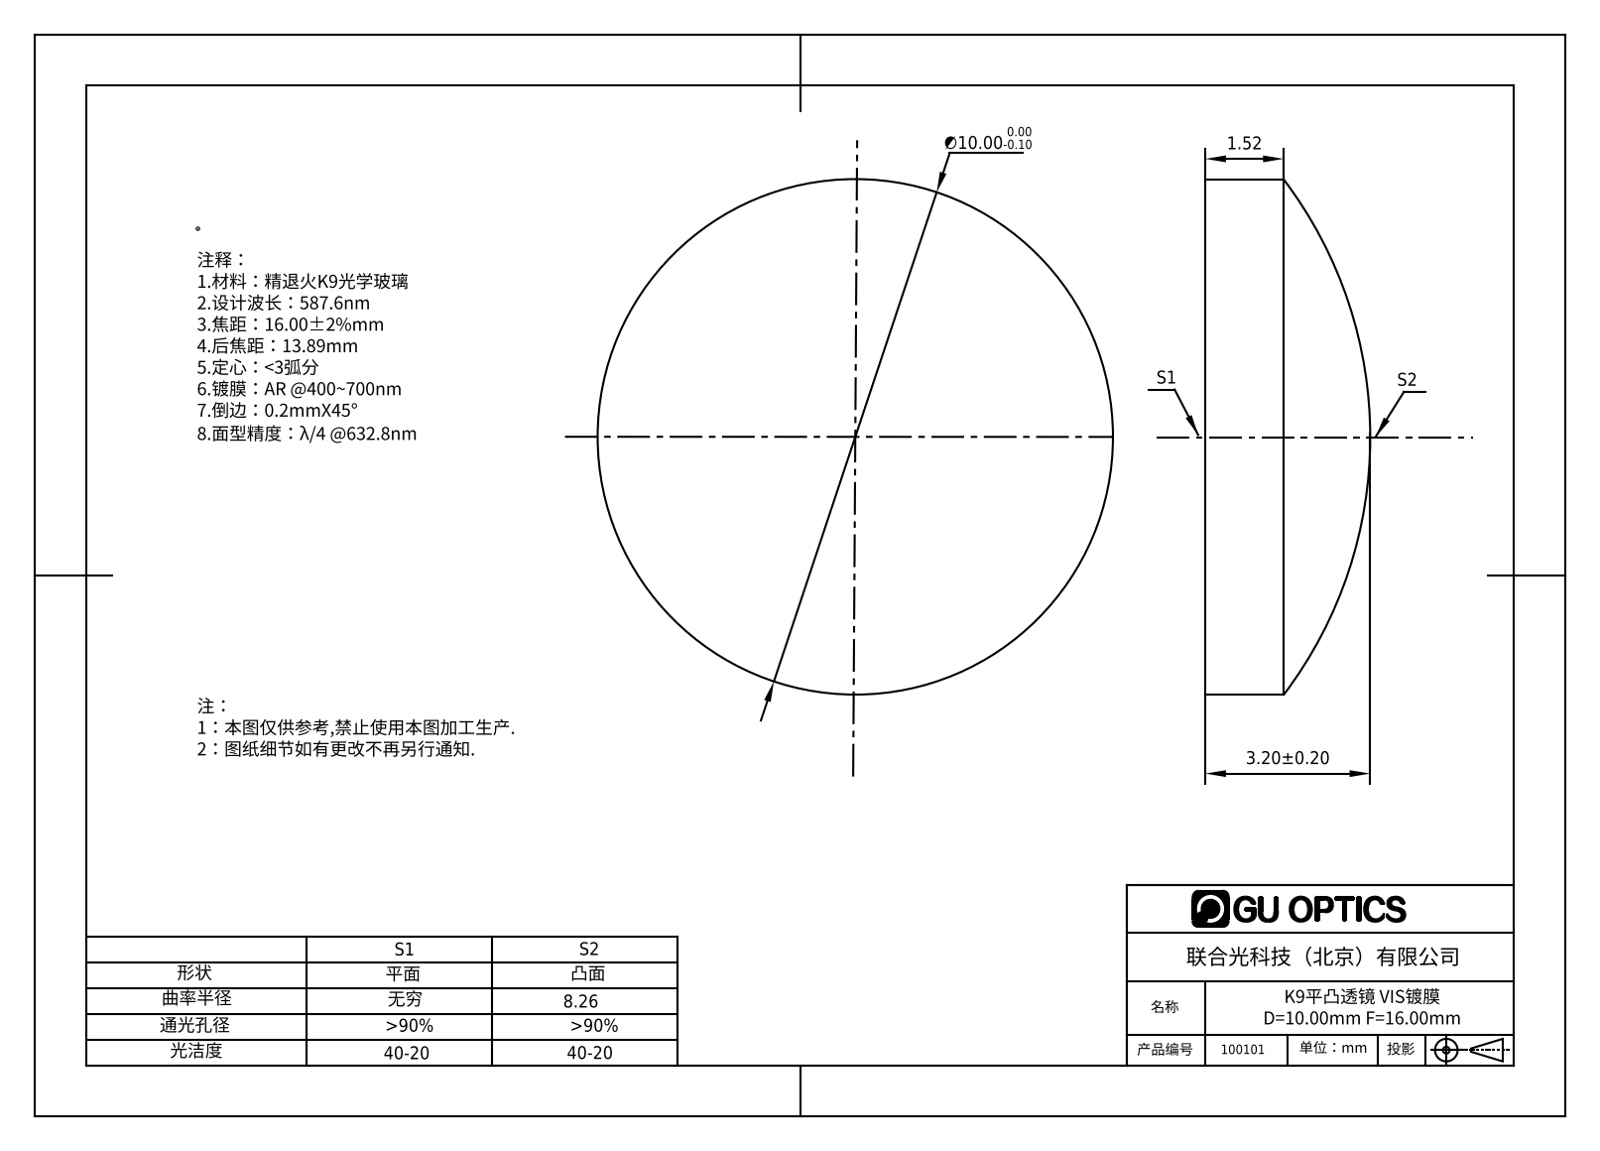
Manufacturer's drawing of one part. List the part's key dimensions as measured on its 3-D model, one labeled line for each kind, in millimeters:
Part name (STEP PRODUCT): 100101
STEP written by: SolidWorks 2016 (AUTOMOTIVE_DESIGN)
Units: millimetres
Bodies: 1 solid, 5 faces (1 planar, 2 cylindrical, 2 other)
Overall size (bounding box): 10 × 10 × 3.2
Volume: 188 mm³ · Surface area: 214 mm²
Round bosses / shafts (diameter × count): ⌀10 ×1
